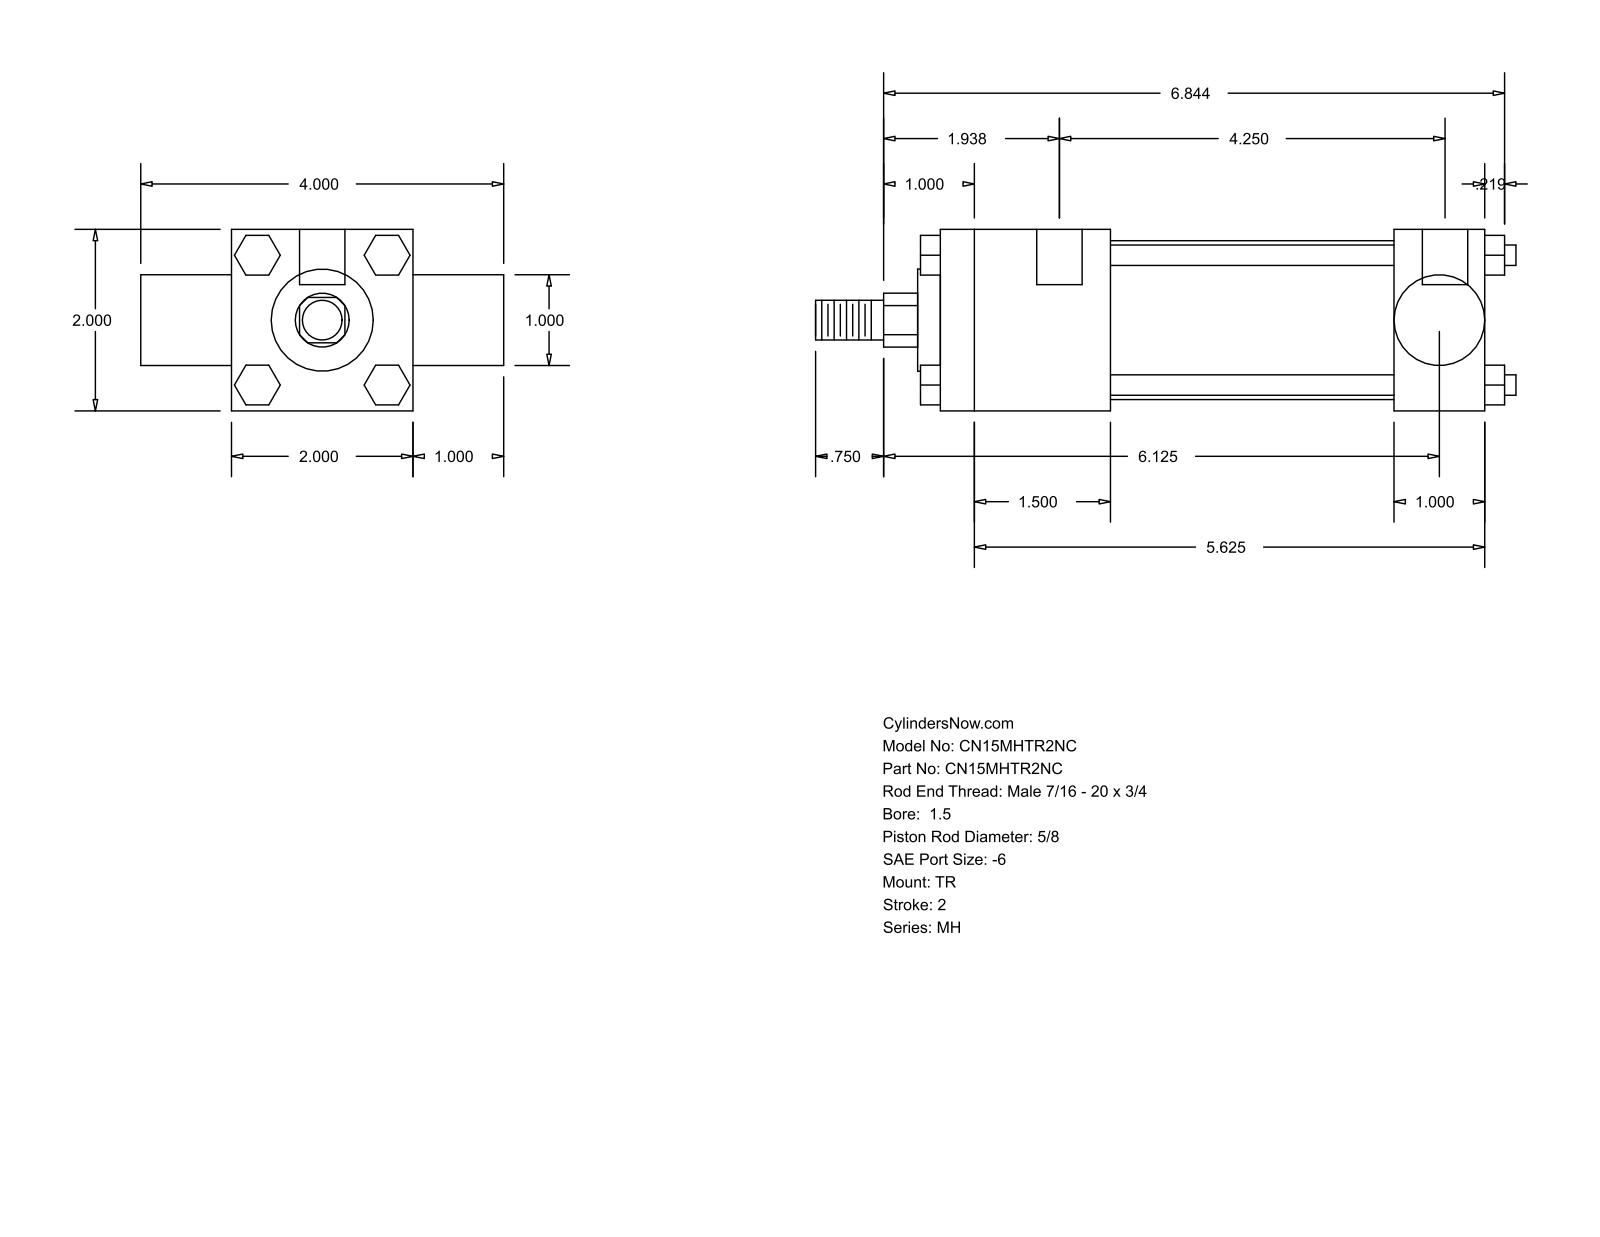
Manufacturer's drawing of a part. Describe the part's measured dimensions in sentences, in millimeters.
The part is named "MH_TR__0150_0.625". Its 3-D file was written by "GSSL Pune (CONFIG_CONTROL_DESIGN)". It is 0 solids with 120 faces: 92 planar, 28 cylindrical and 0 other. Overall it measures 196.06 by 101.6 by 50.8 millimeters. Round holes: 3 of diameter 5.56, 2 of diameter 12.7. Round bosses or shafts: 4 of diameter 5.71, 1 of diameter 44.45, 1 of diameter 28.57, 1 of diameter 25.35, 1 of diameter 15.88, 1 of diameter 11.11. Partial cylindrical surfaces (rounded edges, fillets, slot ends): 1 of radius 7.54. The main face-to-face distances are 50.8, 25.4, 152.4, 76.2, 47.62, 104.78, 127, 79.38, 11.11, 18.16. The hole center spacings are 3.17, 107.95, 111.12.
